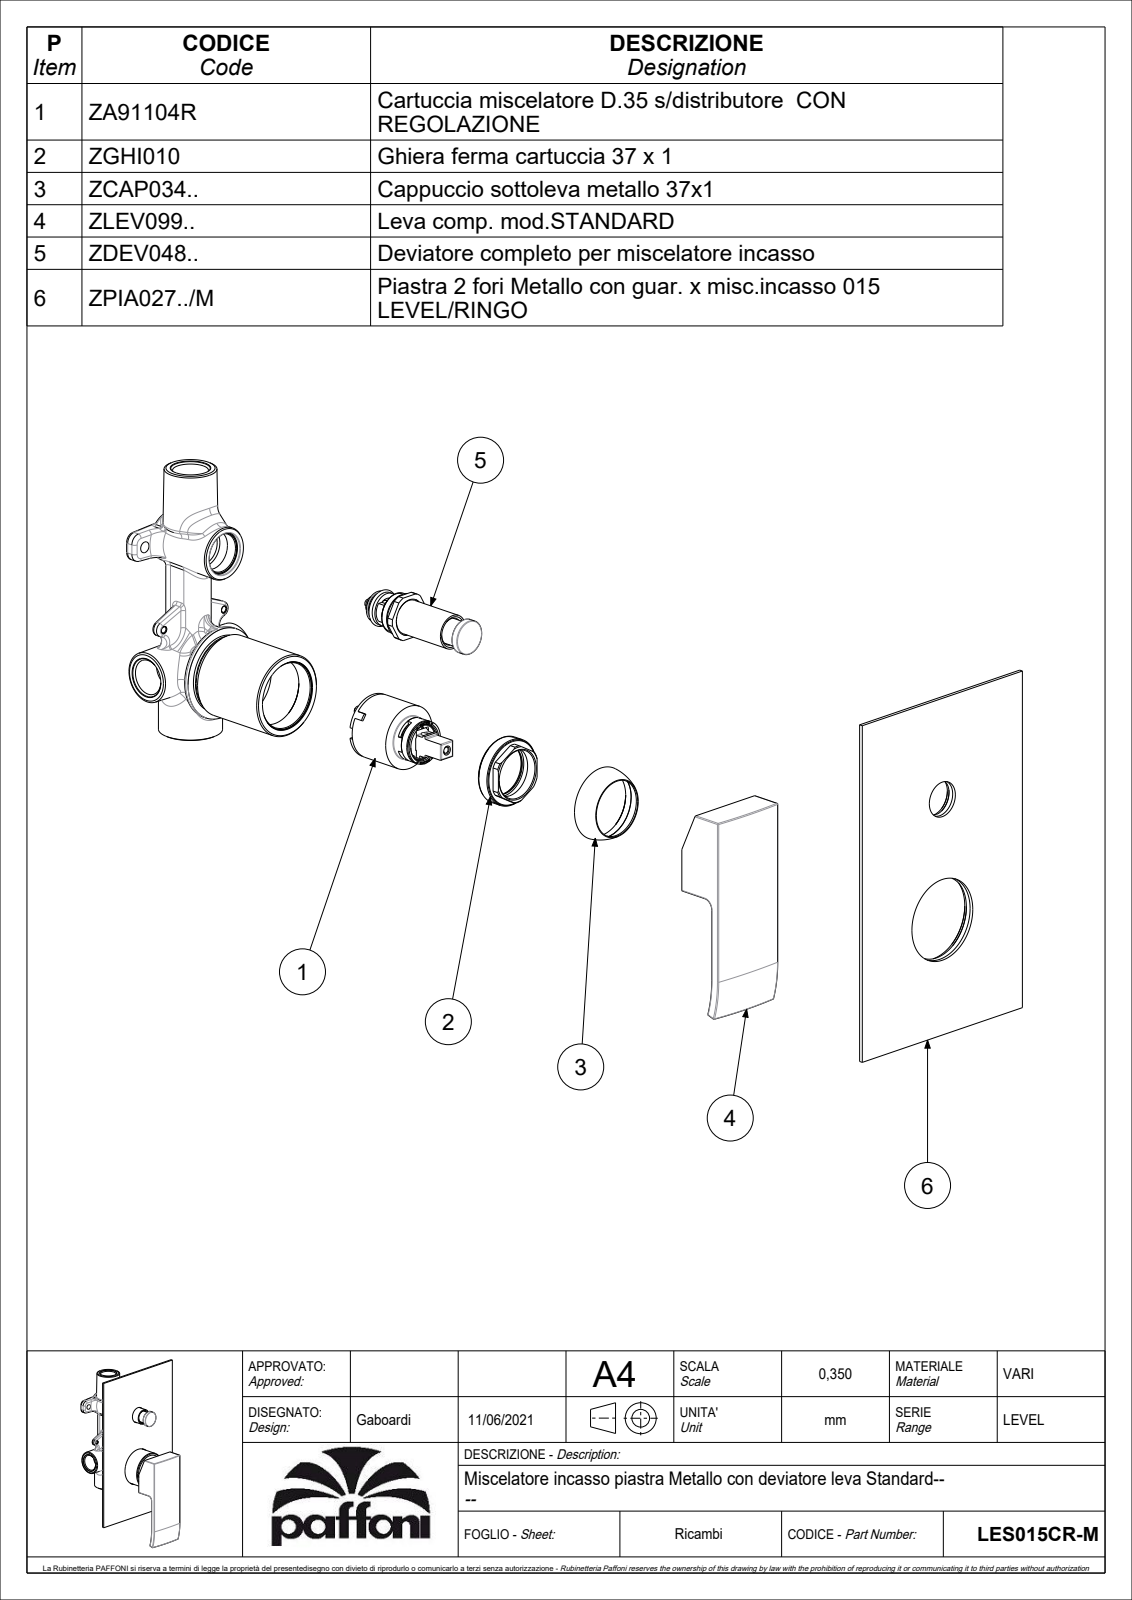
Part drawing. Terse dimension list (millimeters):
name: LES015CR-M
written by: CREO PARAMETRIC BY PTC INC, 2020044 (CONFIG_CONTROL_DESIGN)
unit: mm
bodies: 5 solids, 898 faces (549 planar, 206 cylindrical, 143 other)
size: 213.38 × 120 × 54.05
volume: 103 636 mm³; area: 85 536 mm²
holes: 2× ⌀4, 2× ⌀19.5, 1× ⌀3, 1× ⌀3.3, 1× ⌀5, 1× ⌀5.5, 1× ⌀7.8, 1× ⌀10.5, 1× ⌀14.8, 1× ⌀19.9, 1× ⌀26.8, 1× ⌀29
bosses: 1× ⌀44.8, 1× ⌀35, 1× ⌀23.5, 1× ⌀23.4, 1× ⌀21.8, 1× ⌀18.7, 1× ⌀18.6, 1× ⌀14
rounds: 14× R1.5, 12× R0.5, 11× R0.15, 4× R0.3, 4× R2, 2× R1, 2× R300, 1× R2.25
face distances: 2, 45, 51, 49, 37.5, 82.5, 17.2, 15.2, 33.8, 5.5
hole spacings: 8, 68
